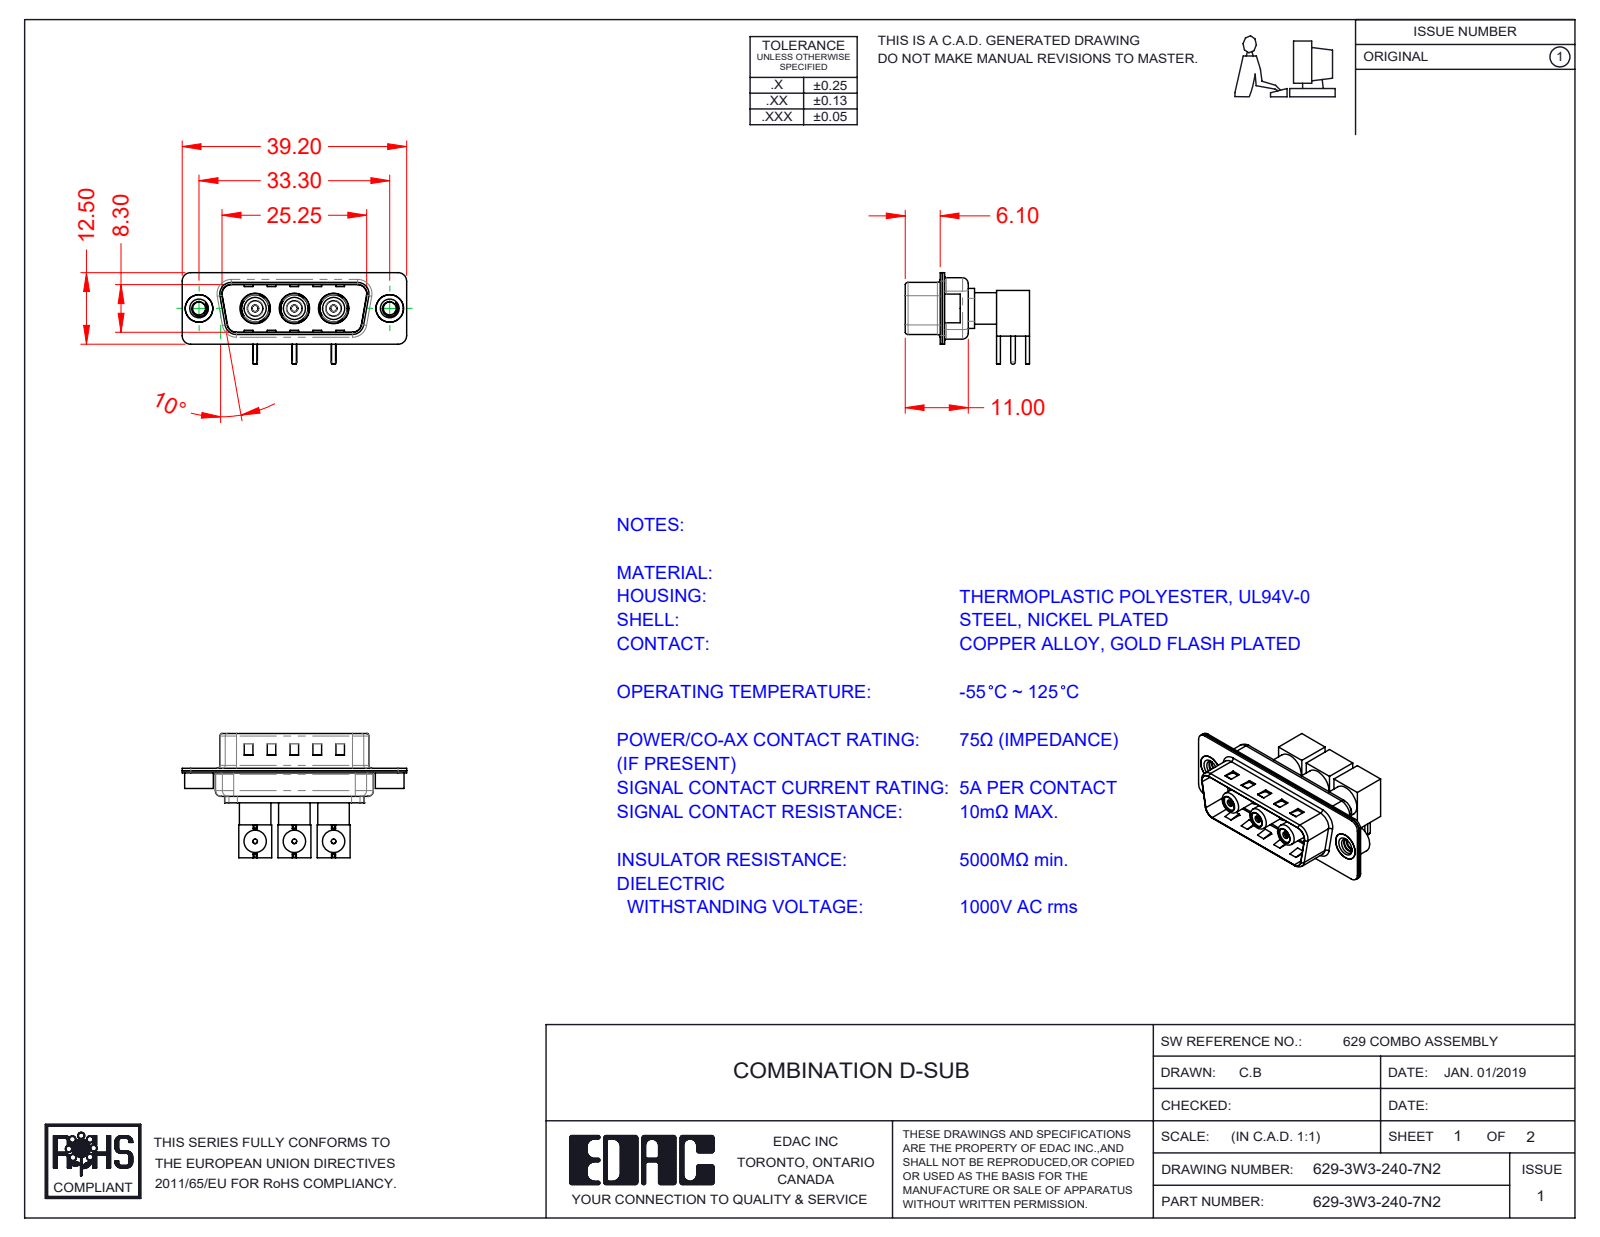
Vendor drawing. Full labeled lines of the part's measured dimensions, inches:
Part name (STEP PRODUCT): Insulator Socket 2; Insulator Socket; 629Combo Housing_3W3; 629Combo Shell Front_15 Contacts (+8 more)
STEP written by: SolidWorks 2020 (CONFIG_CONTROL_DESIGN)
Units: inches
Bodies: 26 solids, 796 faces (310 planar, 334 cylindrical, 152 other)
Overall size (bounding box): 1.543 × 0.855 × 0.63
Volume: 0.165 in³ · Surface area: 11.66 in²
Round holes (diameter × count): ⌀0.031 ×3, ⌀0.043 ×3, ⌀0.047 ×3, ⌀0.059 ×3, ⌀0.063 ×3, ⌀0.098 ×3, ⌀0.106 ×3, ⌀0.122 ×3, ⌀0.134 ×3, ⌀0.154 ×3, ⌀0.161 ×3, ⌀0.191 ×3
Round bosses / shafts (diameter × count): ⌀0.031 ×6, ⌀0.217 ×3, ⌀0.205 ×3, ⌀0.189 ×3, ⌀0.186 ×3, ⌀0.164 ×3, ⌀0.157 ×3, ⌀0.152 ×3
Partial cylindrical surfaces — rounded edges, fillets, slot ends (radius × count): R0.059 ×16, R0.079 ×12, R0.02 ×8, R0.063 ×8, R0.01 ×4, R0.024 ×4, R0.026 ×4, R0.035 ×4
Main face-to-face distances: 0.016, 0.031, 0.226, 0.374, 0.014, 0.27, 0.358, 0.343, 0.055, 0.39
Hole centre spacings: 0.27, 0.539, 0.386, 0.656, 0.925, 1.311
